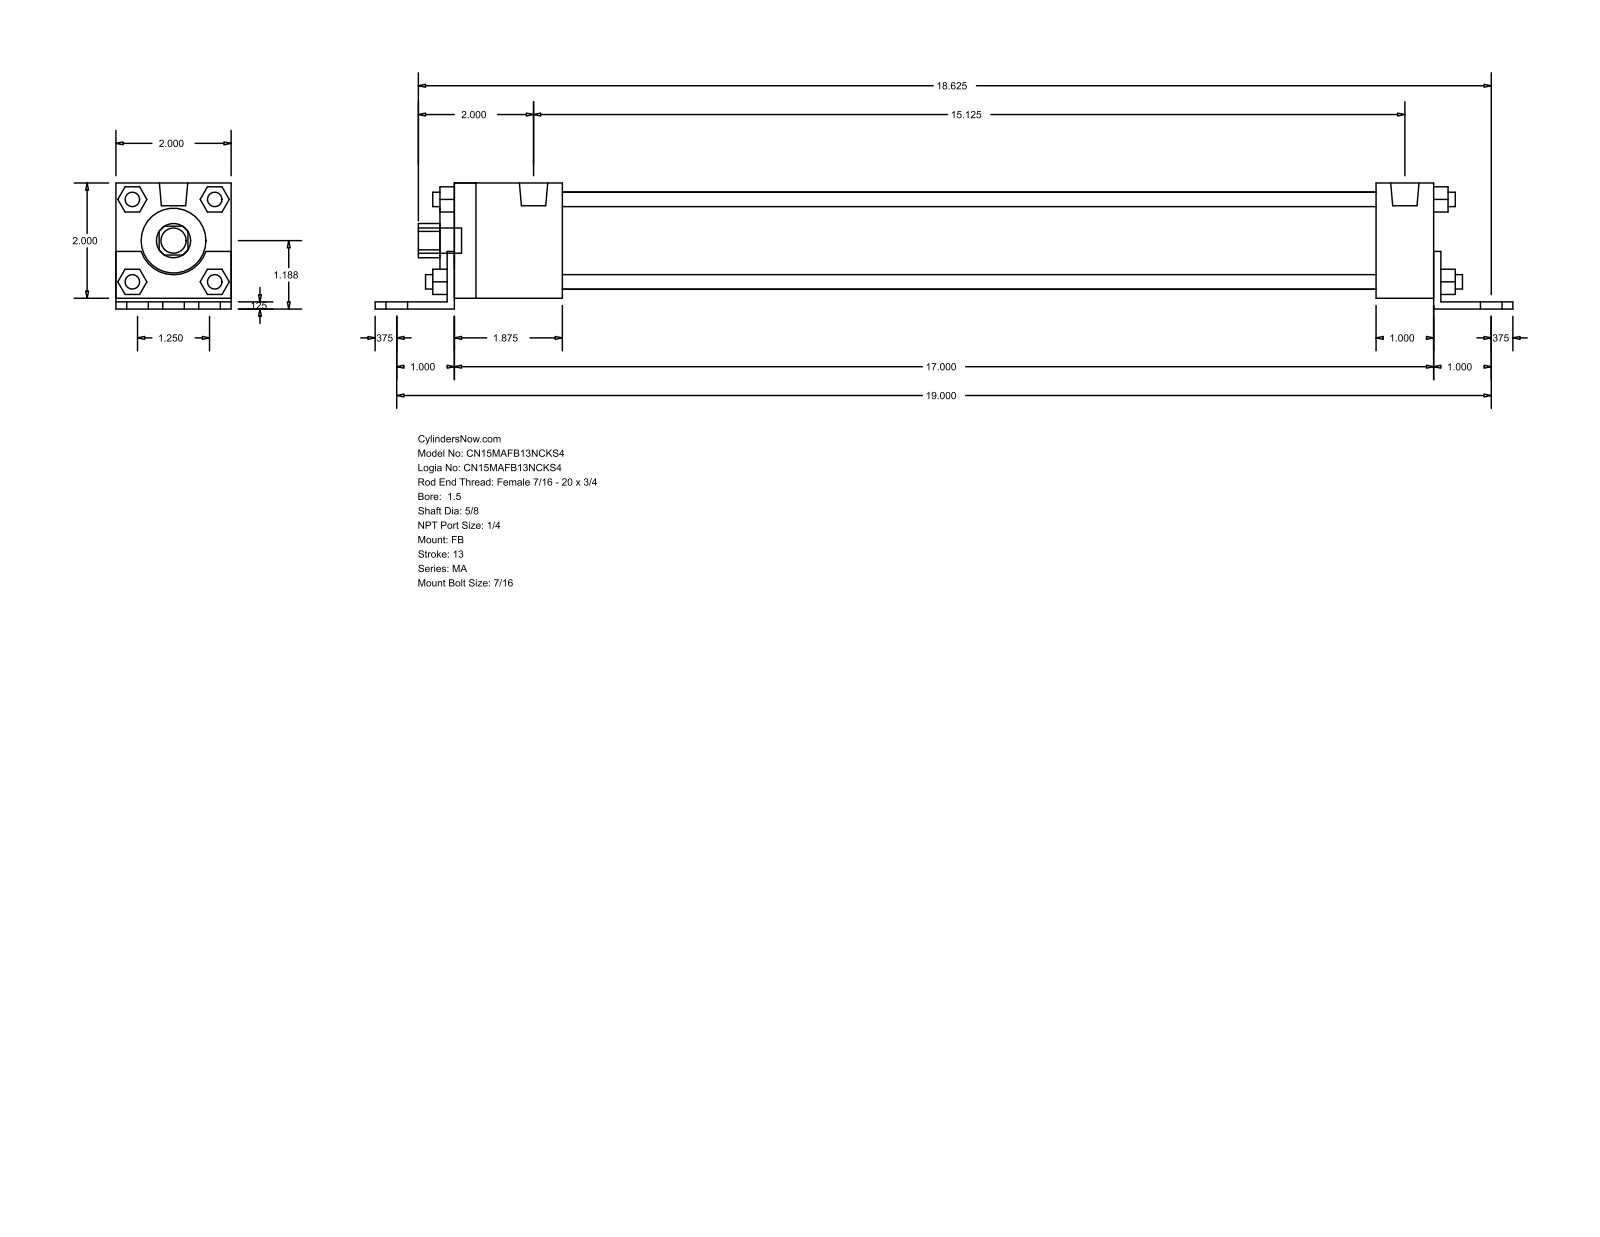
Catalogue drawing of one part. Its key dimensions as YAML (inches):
part_name: "MA_FB__0150_0.625"
step_written_by: "GSSL Pune (CONFIG_CONTROL_DESIGN)"
units: inches
bodies: {solids: 0, faces: 140, planar: 105, cylindrical: 35, other: 0}
overall_size: [19.75, 2.187, 2]
round_holes:
  - {diameter: 0.625, count: 1}
  - {diameter: 1.125, count: 1}
  - {diameter: 1.69, count: 1}
round_bosses_or_shafts:
  - {diameter: 0.437, count: 7}
  - {diameter: 0.313, count: 4}
  - {diameter: 0.25, count: 4}
  - {diameter: 0.492, count: 2}
partial_cylinders:
  - {radius: 0.297, count: 1}
  - {radius: 0.593, count: 1}
face_to_face_distances: [2, 0.125, 0.187, 2.187, 0.063, 2.063, 17.25, 0.125, 17, 1.125]
